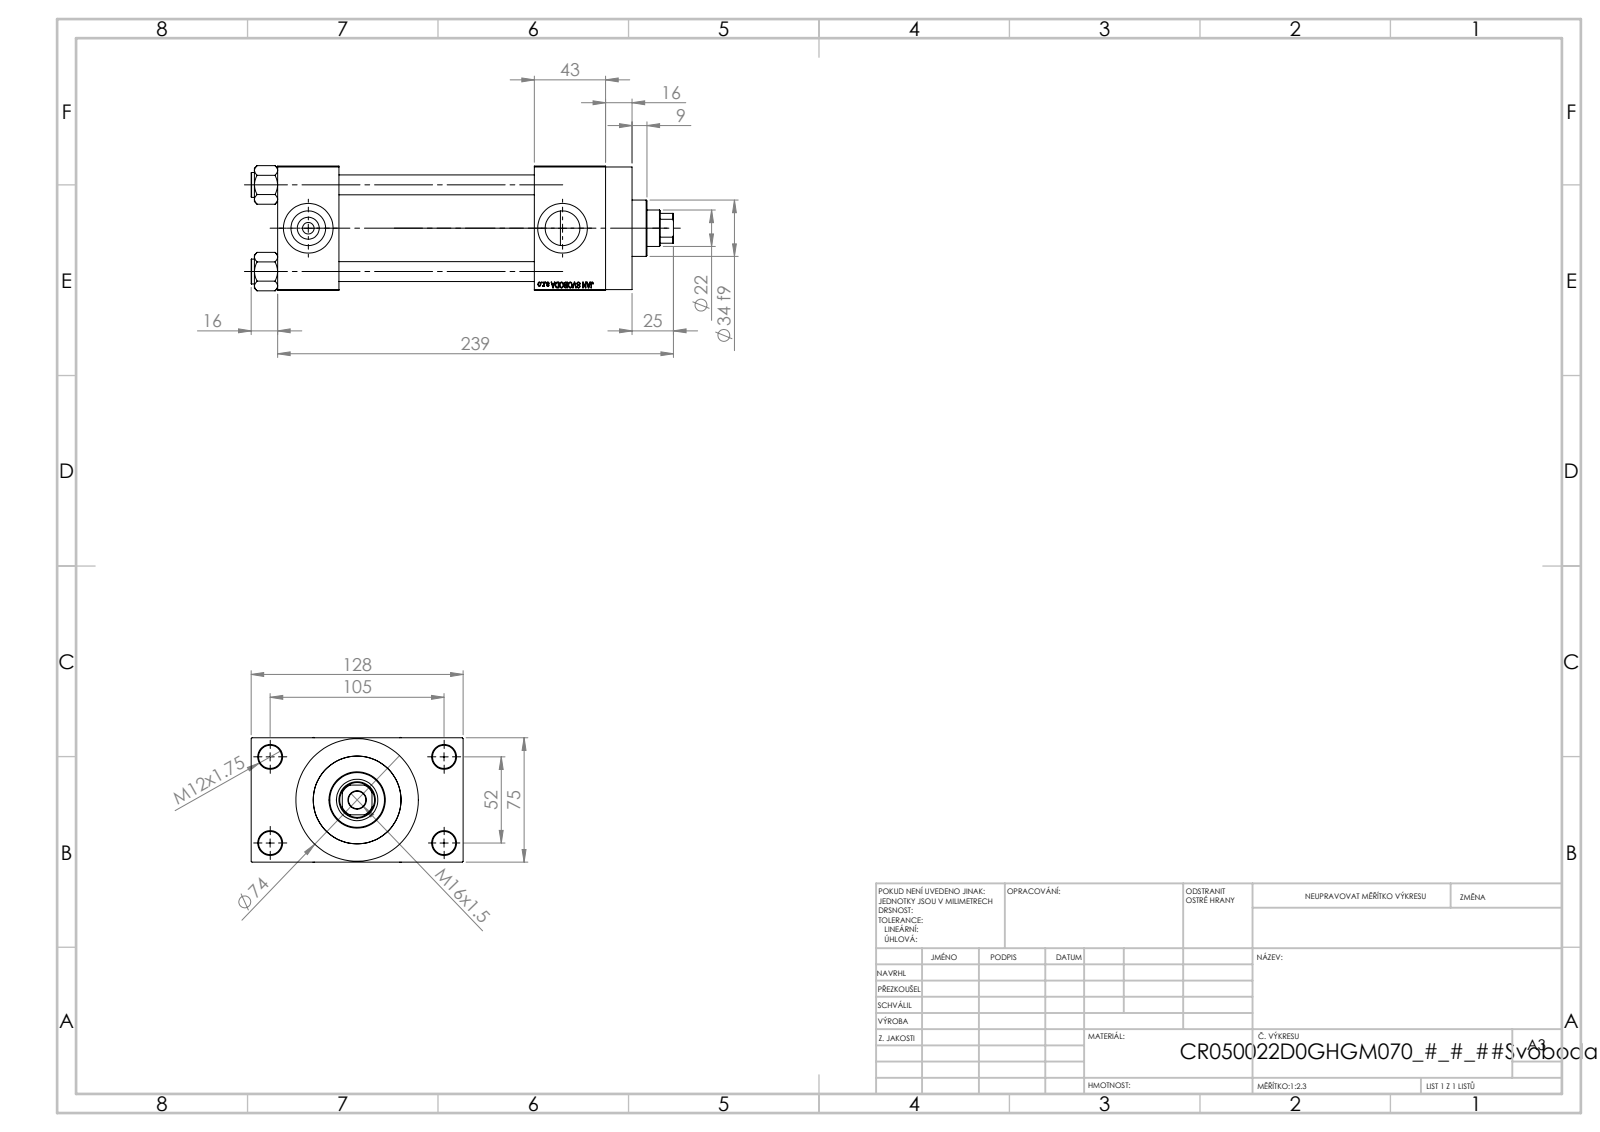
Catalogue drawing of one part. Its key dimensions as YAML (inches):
part_name: "V215_VC_A; V215CR_VCP_D; V215CR_D_Body; NUT_M5_D (+1 more)"
step_written_by: "SolidWorks 2019 (CONFIG_CONTROL_DESIGN)"
units: inches
bodies: {solids: 11, faces: 1103, planar: 497, cylindrical: 88, other: 518}
overall_size: [10.039, 5.039, 2.974]
volume: 53.54
surface_area: 309.8
round_holes:
  - {diameter: 0.472, count: 4}
  - {diameter: 0.551, count: 4}
  - {diameter: 0.276, count: 2}
  - {diameter: 0.825, count: 2}
  - {diameter: 1.181, count: 2}
  - {diameter: 0.413, count: 1}
  - {diameter: 0.866, count: 1}
  - {diameter: 0.984, count: 1}
  - {diameter: 1.614, count: 1}
  - {diameter: 1.969, count: 1}
  - {diameter: 2.087, count: 1}
round_bosses_or_shafts:
  - {diameter: 0.591, count: 4}
  - {diameter: 2.913, count: 1}
  - {diameter: 2.205, count: 1}
  - {diameter: 1.339, count: 1}
partial_cylinders:
  - {radius: 0.413, count: 1}
face_to_face_distances: [2.953, 4.646, 1.457, 6.102, 1.043, 7.795, 6.339, 1.693, 3.996, 0.63]
hole_center_spacings: [1.037, 1.456, 2.059, 2.3, 2.307, 3.096, 3.715, 2.047]
